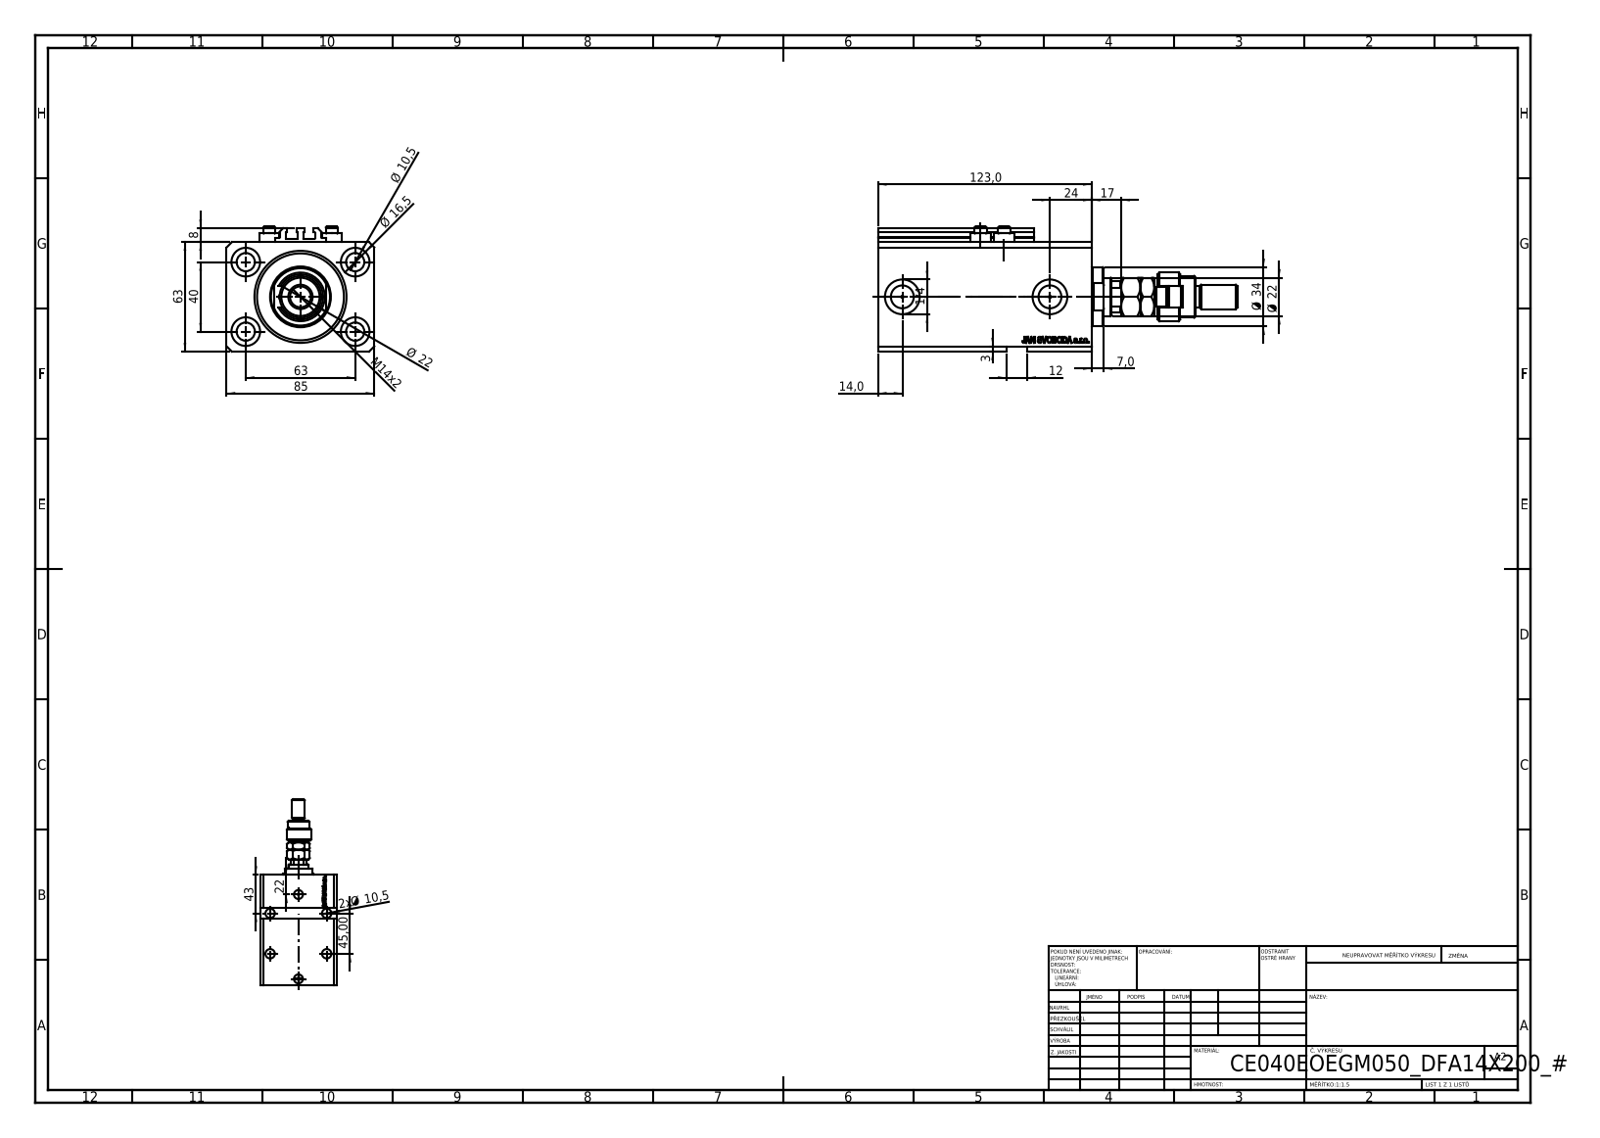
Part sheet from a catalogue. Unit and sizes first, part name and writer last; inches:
Units: inches
Overall size (bounding box): 8.15 × 3.346 × 2.835
Round holes (diameter × count): ⌀0.413 ×8, ⌀0.049 ×4, ⌀0.157 ×4, ⌀0.65 ×4, ⌀0.394 ×2, ⌀0.518 ×2, ⌀0.787 ×2, ⌀0.492 ×1, ⌀0.866 ×1, ⌀1.575 ×1, ⌀2.087 ×1
Round bosses / shafts (diameter × count): ⌀0.457 ×4, ⌀0.276 ×4, ⌀1.339 ×1, ⌀1.102 ×1, ⌀0.945 ×1, ⌀0.709 ×1, ⌀0.551 ×1, ⌀0.472 ×1
Partial cylindrical surfaces — rounded edges, fillets, slot ends (radius × count): R0.008 ×10, R0.384 ×1, R0.413 ×1
Main face-to-face distances: 2.48, 3.346, 0.669, 4.843, 4.173, 0.449, 3.724, 4.394, 0.118, 0.236
Hole centre spacings: 1.469, 2.48, 0.535, 0.606, 0.983, 1.084, 1.324, 1.417
Volume: 35.31 in³ · Surface area: 197.3 in²
Bodies: 10 solids, 1192 faces (563 planar, 159 cylindrical, 470 other)
Part name (STEP PRODUCT): V250CE_VC_E; ALLEN BOLT V250CE; MFA; FEMALE_PART_FOR_DFA (+2 more)
STEP written by: SolidWorks 2019 (CONFIG_CONTROL_DESIGN)
